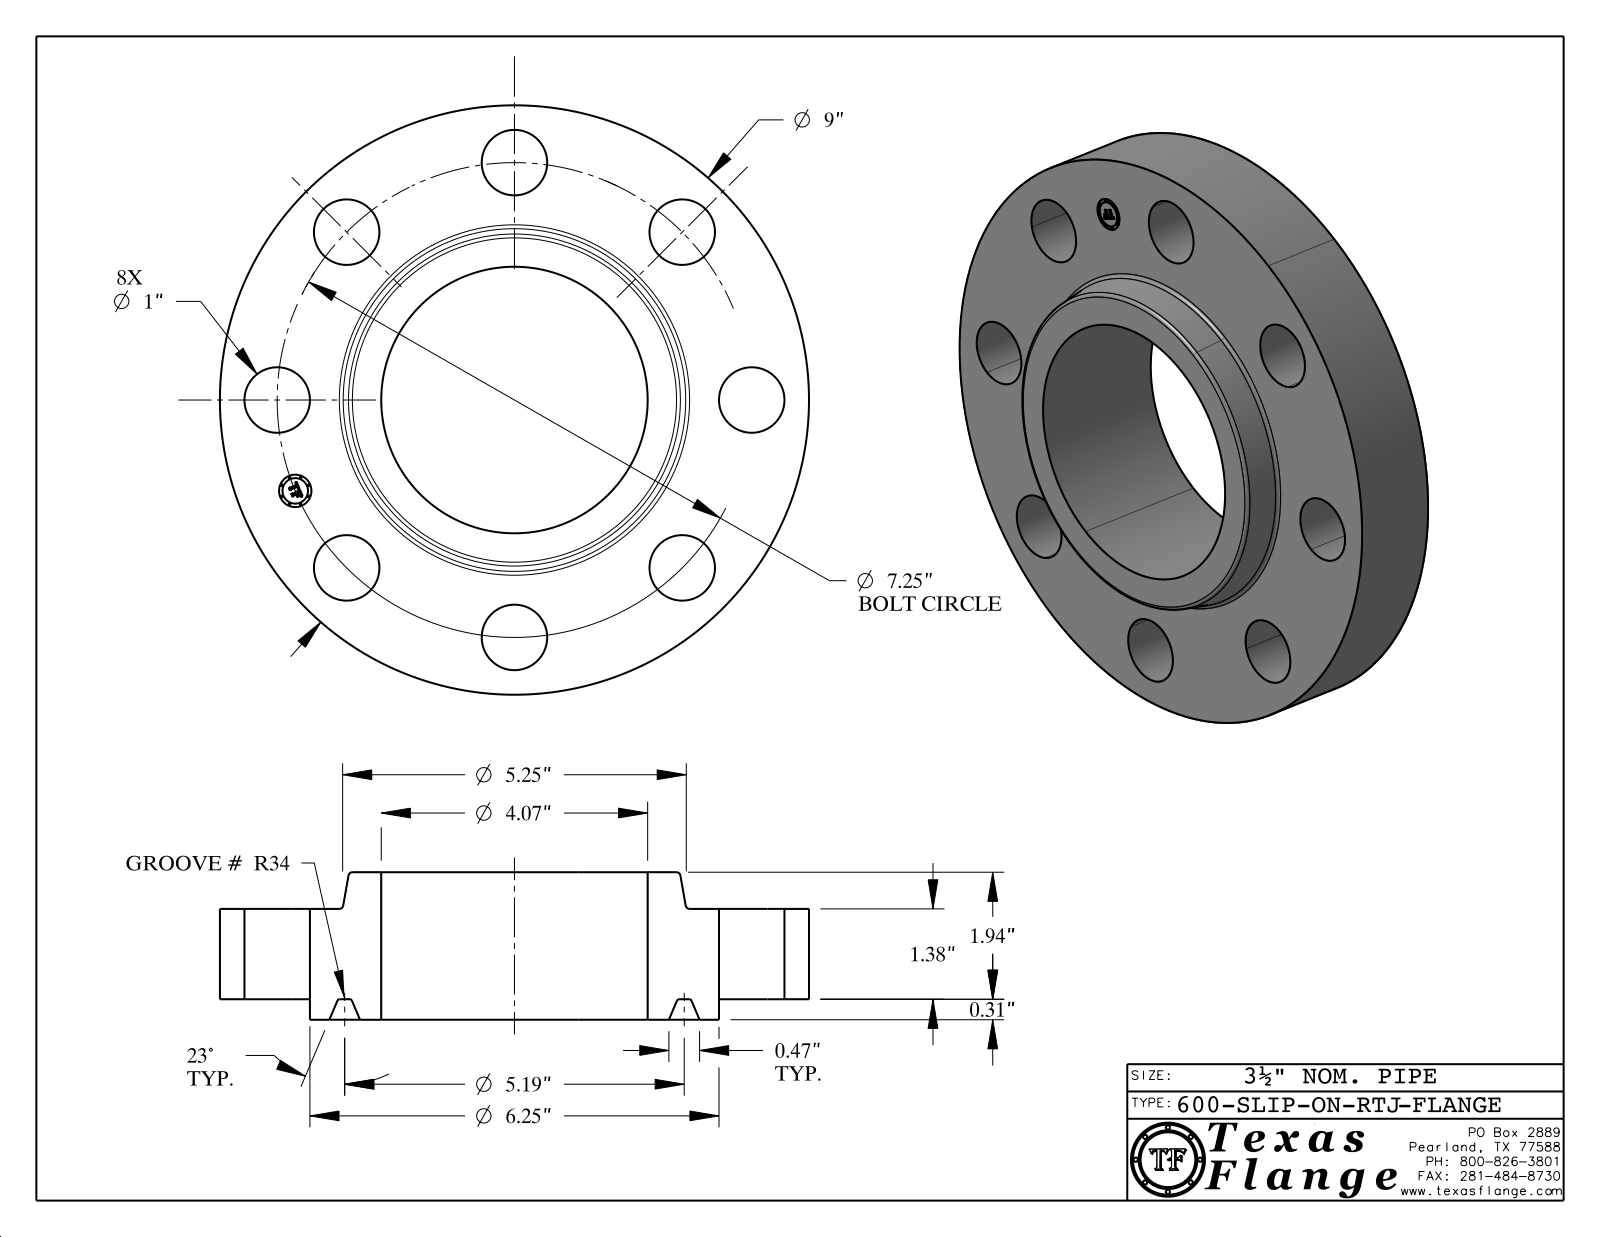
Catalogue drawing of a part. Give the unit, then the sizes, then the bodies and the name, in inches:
Units: inches
Overall size (bounding box): 9 × 9 × 2.253
Round holes (diameter × count): ⌀1 ×8, ⌀0.495 ×1, ⌀4.07 ×1
Round bosses / shafts (diameter × count): ⌀0.03 ×8, ⌀9 ×1, ⌀6.25 ×1, ⌀0.39 ×1
Main face-to-face distances: 1.38, 0.313, 1.693, 2.253, 1.94, 0.56, 1.678, 1.365, 0.015, 0.575
Hole centre spacings: 3.625, 2.774, 5.127, 6.698, 7.25, 1.415, 7.111, 4.028
Volume: 69.37 in³ · Surface area: 211 in²
Bodies: 1 solid, 427 faces (371 planar, 42 cylindrical, 14 other)
Part name (STEP PRODUCT): 600-SLIP-ON-RTJ
STEP written by: CATIA V5 STEP AP214 (AUTOMOTIVE_DESIGN)
